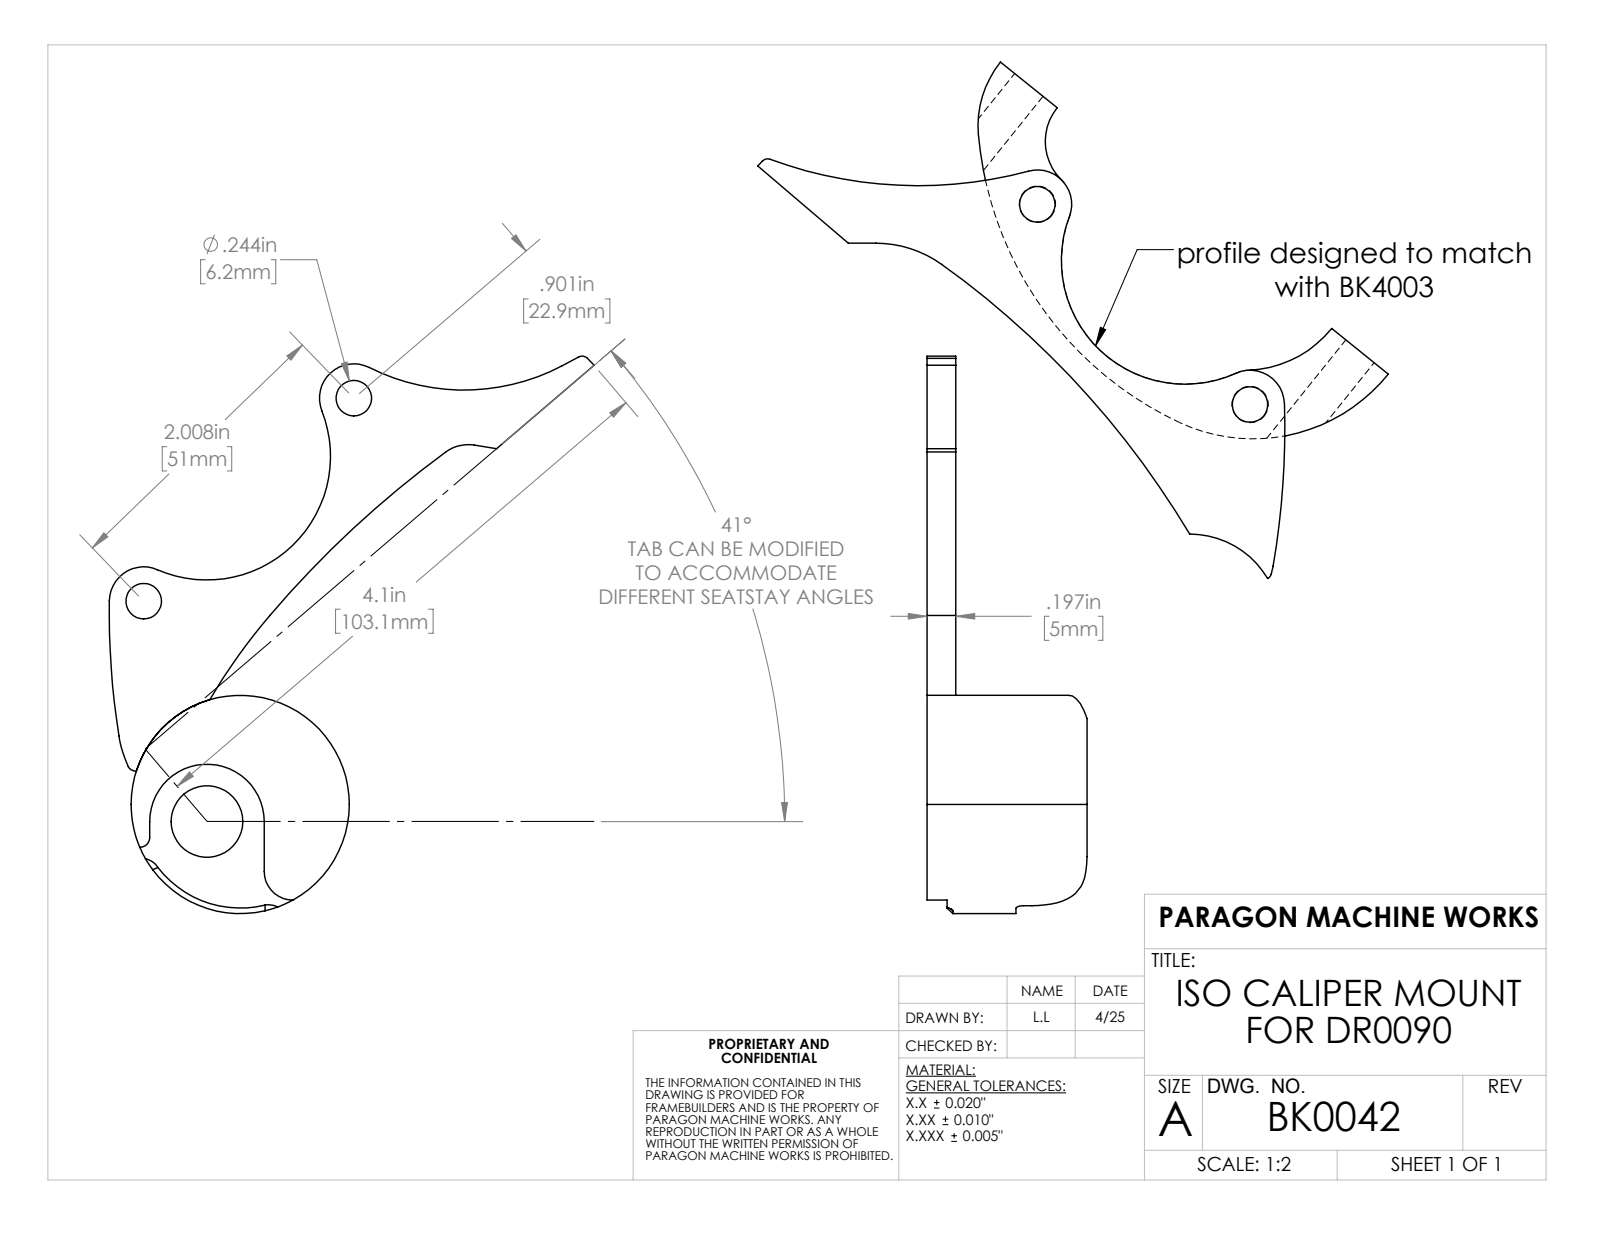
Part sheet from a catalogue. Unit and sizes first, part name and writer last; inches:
Units: inches
Overall size (bounding box): 3.333 × 2.854 × 0.22
Round holes (diameter × count): ⌀0.244 ×2
Partial cylindrical surfaces — rounded edges, fillets, slot ends (radius × count): R0.05 ×2, R0.236 ×2, R0.264 ×1, R0.69 ×1, R0.75 ×1, R0.787 ×1, R0.85 ×1, R1.446 ×1
Main face-to-face distances: 0.22
Hole centre spacings: 2.008
Volume: 0.436 in³ · Surface area: 6.558 in²
Bodies: 1 solid, 29 faces (8 planar, 21 cylindrical, 0 other)
Part name (STEP PRODUCT): BK0042
STEP written by: SolidWorks 2019 (AUTOMOTIVE_DESIGN)
